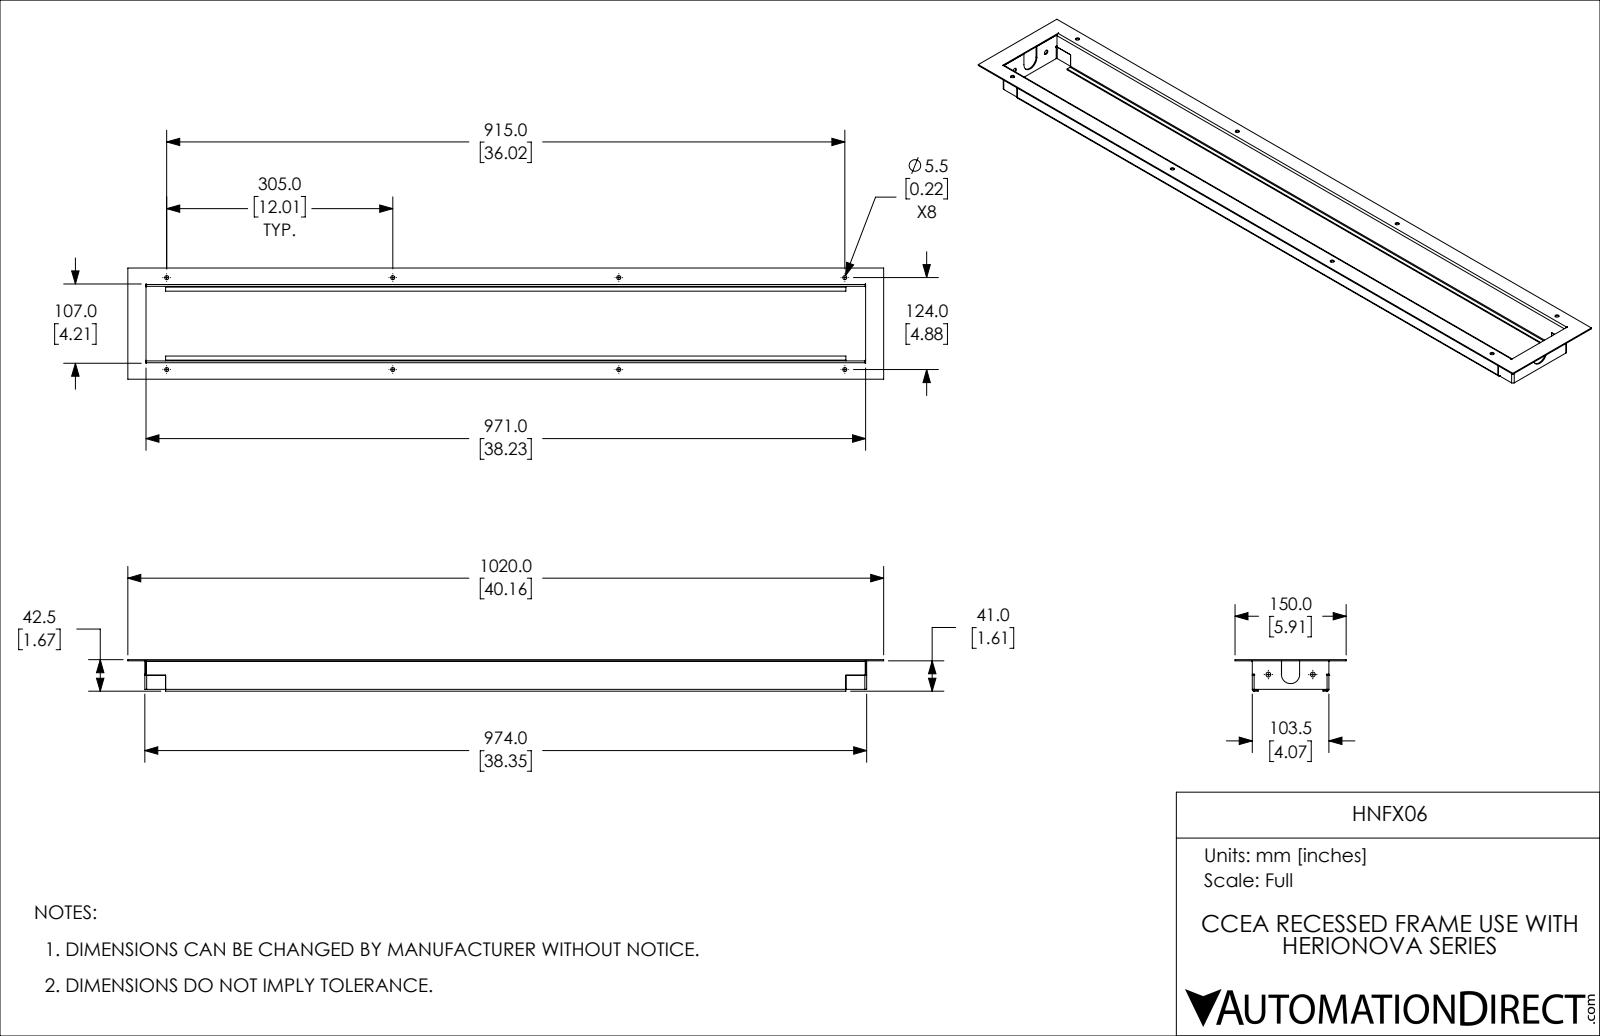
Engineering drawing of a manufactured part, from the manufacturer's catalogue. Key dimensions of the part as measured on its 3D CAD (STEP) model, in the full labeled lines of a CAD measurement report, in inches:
Part name (STEP PRODUCT): HNFX06
STEP written by: SolidWorks 2021 (CONFIG_CONTROL_DESIGN)
Units: inches
Bodies: 3 solids, 146 faces (100 planar, 46 cylindrical, 0 other)
Overall size (bounding box): 40.157 × 5.906 × 1.673
Volume: 13.73 in³ · Surface area: 478.6 in²
Round holes (diameter × count): ⌀0.217 ×8, ⌀0.256 ×2
Partial cylindrical surfaces — rounded edges, fillets, slot ends (radius × count): R0.039 ×8, R0.098 ×8, R0.482 ×1
Main face-to-face distances: 0.059, 4.016, 4.075, 3.957, 1.614, 1.555, 1.673, 38.287, 38.228, 38.346
Hole centre spacings: 12.008, 12.962, 4.882, 24.016, 24.507, 36.024, 36.353, 2.362
